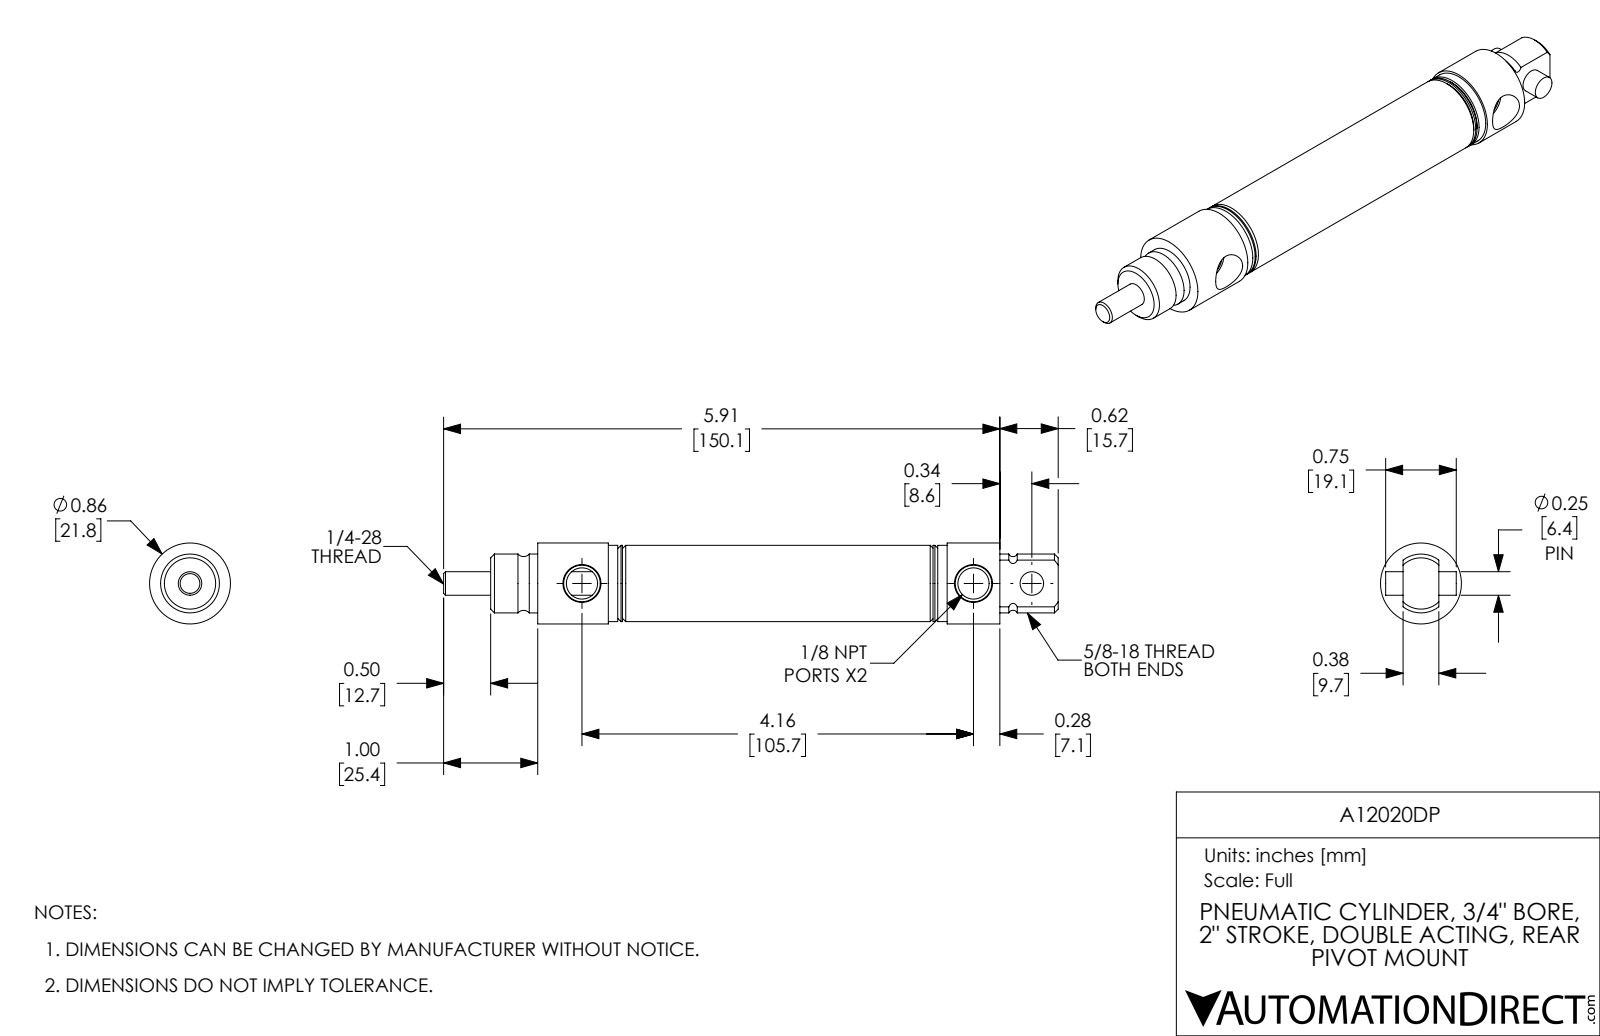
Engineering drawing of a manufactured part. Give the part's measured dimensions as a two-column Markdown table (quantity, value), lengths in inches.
| quantity | value |
| --- | --- |
| part name | A12020DP-PIN; A12020DP-Rod; A12020DP-MainBody; A12020DP |
| STEP written by | SolidWorks 2017 (AUTOMOTIVE_DESIGN) |
| units | inches |
| bodies | 3 solids, 91 faces (21 planar, 38 cylindrical, 32 other) |
| overall size | 6.53 × 0.86 × 0.86 |
| volume | 2.061 in³ |
| surface area | 31.47 in² |
| round holes (diameter × count) | 0.25 × 2, 0.332 × 2, 0.75 × 1 |
| round bosses / shafts (diameter × count) | 0.86 × 1, 0.81 × 1, 0.625 × 1 |
| main face-to-face distances | 0.5, 3.705, 2.5, 2, 1.205, 1.705, 3.705, 4.91, 3.205, 1.205 |
| hole center spacings | 0.62, 4.16, 4.78 |
